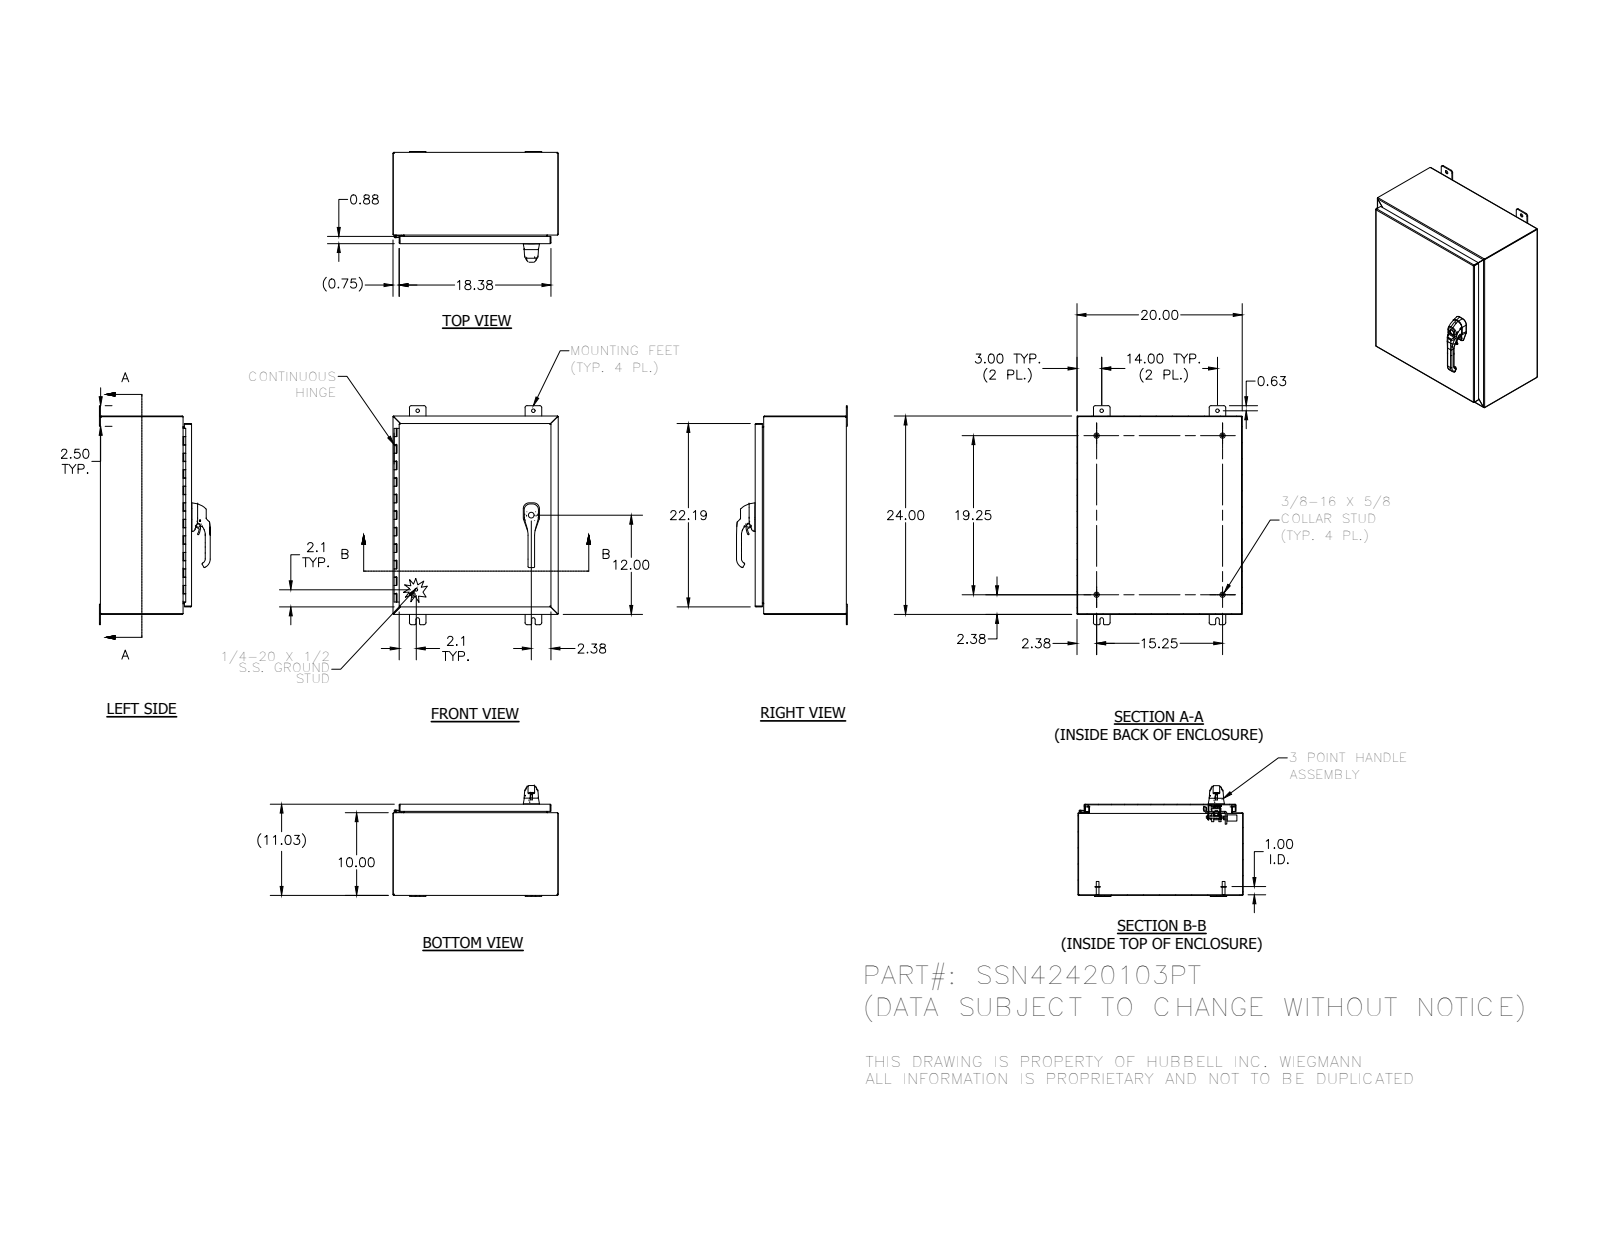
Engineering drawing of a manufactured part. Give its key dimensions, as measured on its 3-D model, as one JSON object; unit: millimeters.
{"part_name": "1000-02; 22x18; SPACER; 328138T (+8 more)", "step_written_by": "SolidWorks 2014 (AUTOMOTIVE_DESIGN)", "units": "millimeters", "bodies": {"solids": 56, "faces": 3059, "planar": 1014, "cylindrical": 1260, "other": 785}, "overall_size": [673.1, 508, 340.6], "volume_mm3": 2887000, "surface_area_mm2": 2919000, "round_holes": [[6.7, 8], [4.7, 4], [11.1, 4], [5.4, 3], [7.1, 3], [6.1, 2], [6.4, 2], [6.4, 2], [8, 2], [10.2, 2], [10.2, 2], [10.5, 2]], "round_bosses_or_shafts": [[15.9, 4], [8.4, 4], [6, 3], [25.4, 2], [14.3, 2], [13.5, 2], [13.5, 2], [12.7, 2]], "partial_cylinders_radius": [[0.5, 172], [0.3, 113], [3.2, 26], [0.8, 24], [0.5, 21], [2.7, 20], [6.4, 20], [0.6, 16]], "face_to_face_distances": [1.9, 278.4, 506.1, 276.5, 280.2, 607.7, 508, 504.2, 252.1, 26.2], "hole_center_spacings": [9.7, 12.5, 19.3, 22.5, 366.5, 5.9, 6.6, 9.7]}
